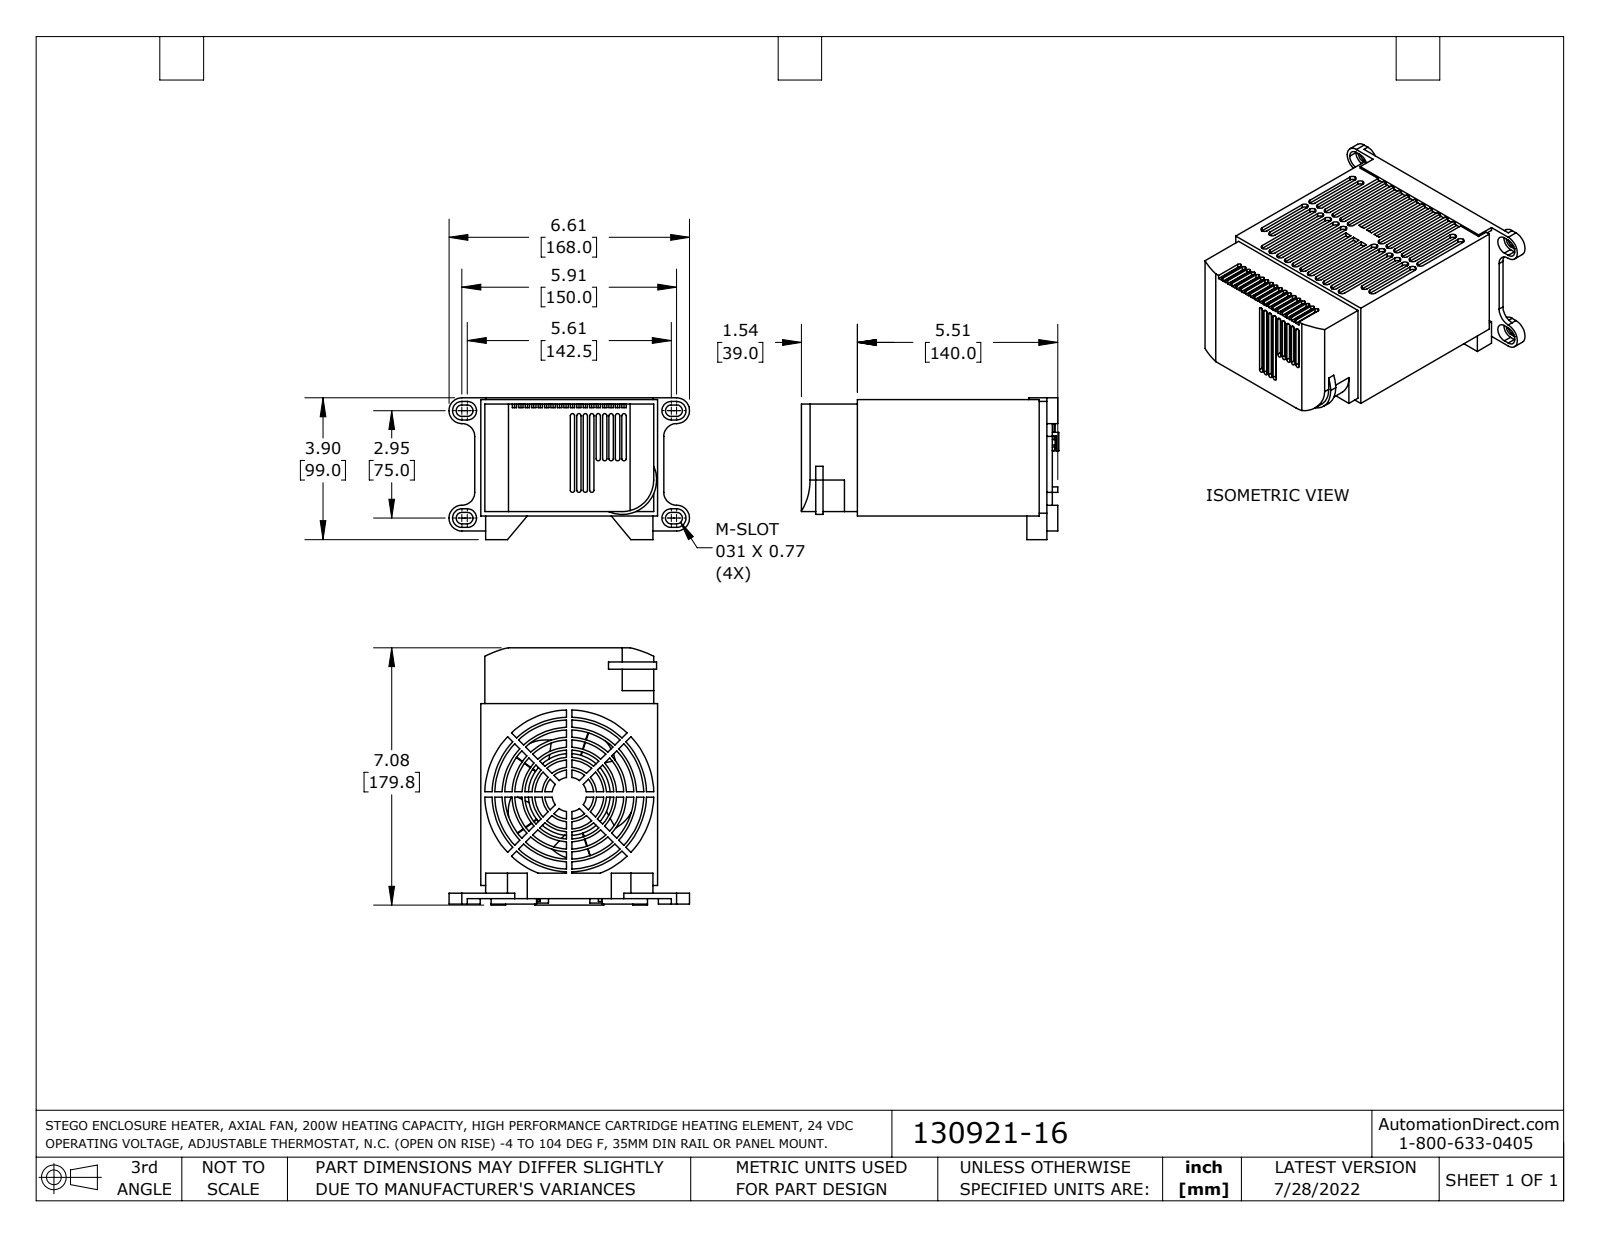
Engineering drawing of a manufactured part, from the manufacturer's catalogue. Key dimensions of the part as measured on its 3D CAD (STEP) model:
Part name (STEP PRODUCT): 130921-16_Default
STEP written by: SolidWorks 2021 (CONFIG_CONTROL_DESIGN)
Units: inches
Bodies: 1 solid, 810 faces (531 planar, 267 cylindrical, 12 other)
Overall size (bounding box): 7.077 × 6.614 × 3.898
Volume: 86.74 in³ · Surface area: 272.5 in²
Round holes (diameter × count): ⌀0.394 ×1, ⌀1.35 ×1, ⌀1.9 ×1, ⌀2.45 ×1, ⌀3 ×1, ⌀3.55 ×1, ⌀4.1 ×1, ⌀4.65 ×1
Round bosses / shafts (diameter × count): ⌀4.25 ×1, ⌀3.7 ×1, ⌀3.15 ×1, ⌀2.6 ×1, ⌀2.25 ×1, ⌀2.05 ×1, ⌀1.5 ×1, ⌀0.95 ×1
Partial cylindrical surfaces — rounded edges, fillets, slot ends (radius × count): R0.1 ×54, R0.059 ×36, R0.354 ×12, R0.157 ×8, R0.256 ×8, R0.05 ×5, R1.086 ×5, R0.13 ×2
Main face-to-face distances: 0.15, 0.1, 2.1, 4.86, 0.212, 0.362, 3.1, 1, 0.124, 2.2
